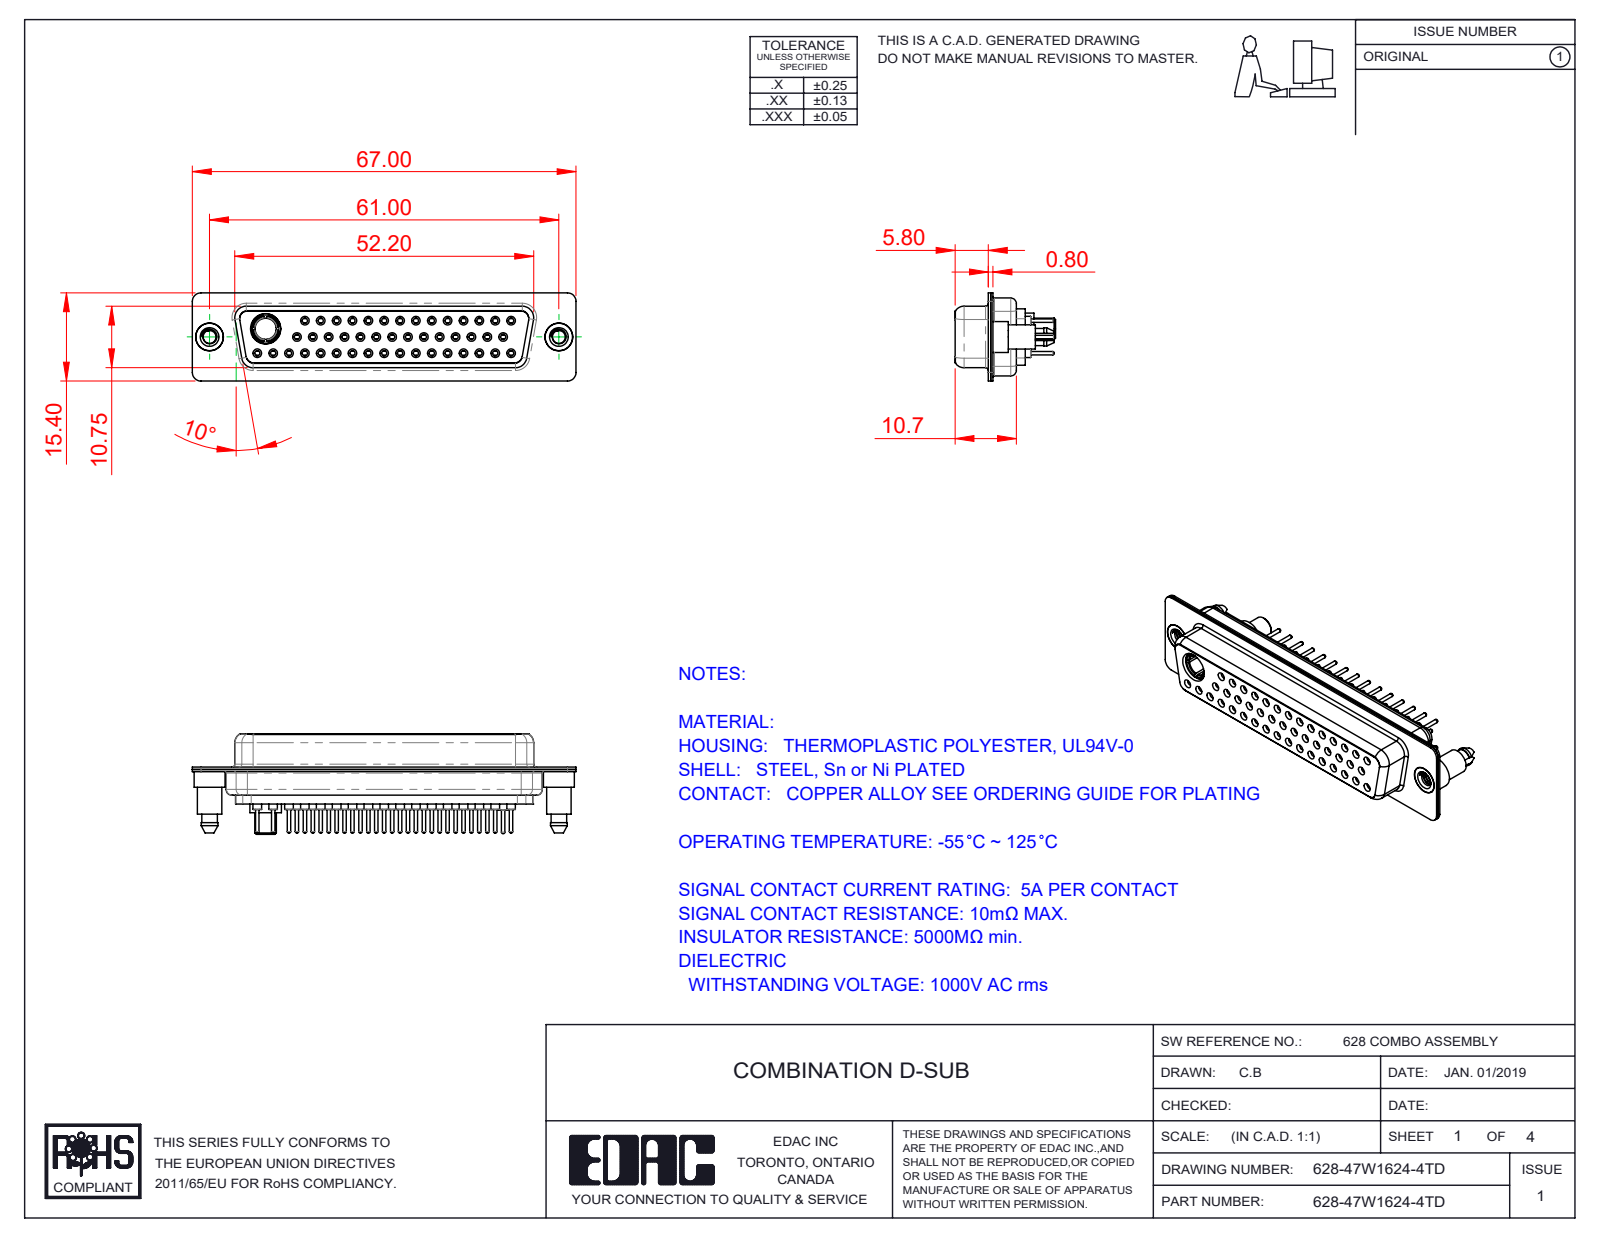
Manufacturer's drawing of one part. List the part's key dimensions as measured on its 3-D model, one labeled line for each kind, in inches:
Part name (STEP PRODUCT): 628Combo Housing_47W1; 628Combo Shell Rear_50 Contacts; 628Combo Contact Row 2_24; 628Combo Shell Front_50 Contacts (+5 more)
STEP written by: SolidWorks 2016 (CONFIG_CONTROL_DESIGN)
Units: inches
Bodies: 53 solids, 2937 faces (799 planar, 1074 cylindrical, 1064 other)
Overall size (bounding box): 2.638 × 0.691 × 0.606
Volume: 0.442 in³ · Surface area: 23.31 in²
Round holes (diameter × count): ⌀0.043 ×46, ⌀0.035 ×45, ⌀0.059 ×45, ⌀0.079 ×45, ⌀0.063 ×31, ⌀0.067 ×14, ⌀0.191 ×3, ⌀0.089 ×2, ⌀0.157 ×2, ⌀0.159 ×2, ⌀0.146 ×1, ⌀0.209 ×1
Round bosses / shafts (diameter × count): ⌀0.087 ×46, ⌀0.024 ×46, ⌀0.063 ×15, ⌀0.213 ×2, ⌀0.195 ×2, ⌀0.189 ×2, ⌀0.167 ×2, ⌀0.217 ×1
Partial cylindrical surfaces — rounded edges, fillets, slot ends (radius × count): R0.059 ×18, R0.053 ×12, R0.079 ×12, R0.063 ×10, R0.01 ×4, R0.02 ×4, R0.024 ×4, R0.026 ×4
Main face-to-face distances: 0.016, 0.446, 0.254, 0.238, 0.074, 0.482, 0.244, 0.228, 0.407, 0.43
Hole centre spacings: 0.124, 0.109, 0.218, 0.327, 0.436, 0.545, 0.654, 0.763
